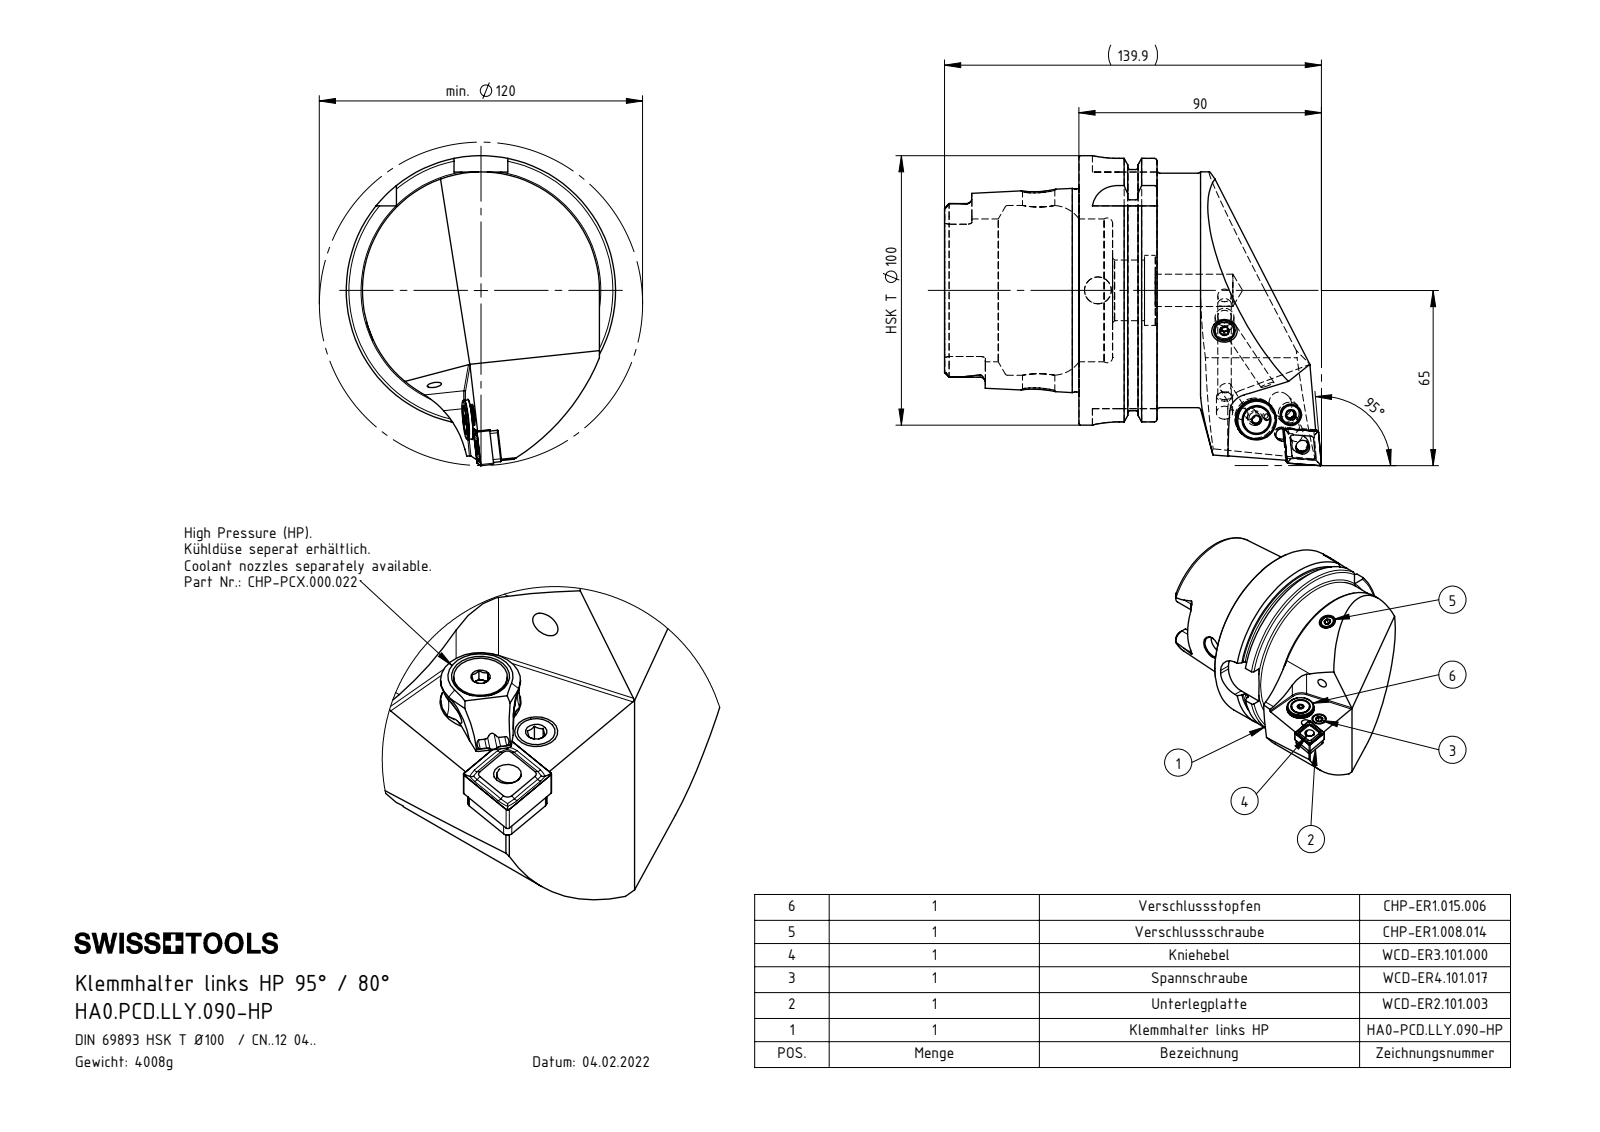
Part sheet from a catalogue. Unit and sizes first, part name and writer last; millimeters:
Units: millimetres
Overall size (bounding box): 139.9 × 115 × 100
Round holes (diameter × count): ⌀5 ×4, ⌀4.2 ×2, ⌀7 ×2, ⌀12 ×2, ⌀1.2 ×1, ⌀2 ×1, ⌀2.5 ×1, ⌀3 ×1, ⌀5.16 ×1, ⌀5.2 ×1, ⌀6 ×1, ⌀6.4 ×1
Round bosses / shafts (diameter × count): ⌀8 ×2, ⌀100 ×1, ⌀91.95 ×1, ⌀87 ×1, ⌀75.26 ×1, ⌀15 ×1, ⌀13.4 ×1, ⌀10 ×1
Partial cylindrical surfaces — rounded edges, fillets, slot ends (radius × count): R1.9 ×6, R0.4 ×4, R1 ×4, R10 ×4, R0.5 ×2, R2.5 ×2, R4.83 ×2, R4.88 ×2
Main face-to-face distances: 12.45, 28.95, 16.5, 49.9, 62.35, 78.85, 87.8, 78.2, 28.3, 15.85
Hole centre spacings: 4.5, 2.25, 8.62, 13.11, 16.86, 20.31, 20.38, 9.26
Volume: 509 659 mm³ · Surface area: 72 154 mm²
Bodies: 12 solids, 507 faces (156 planar, 142 cylindrical, 209 other)
Part name (STEP PRODUCT): CHP-ER1.015.006; DIN 7991 - M5x15; KVT_MB_600_060; DIN 3771 - 13x1 (+8 more)
STEP written by: SolidWorks 2017 (AUTOMOTIVE_DESIGN)
